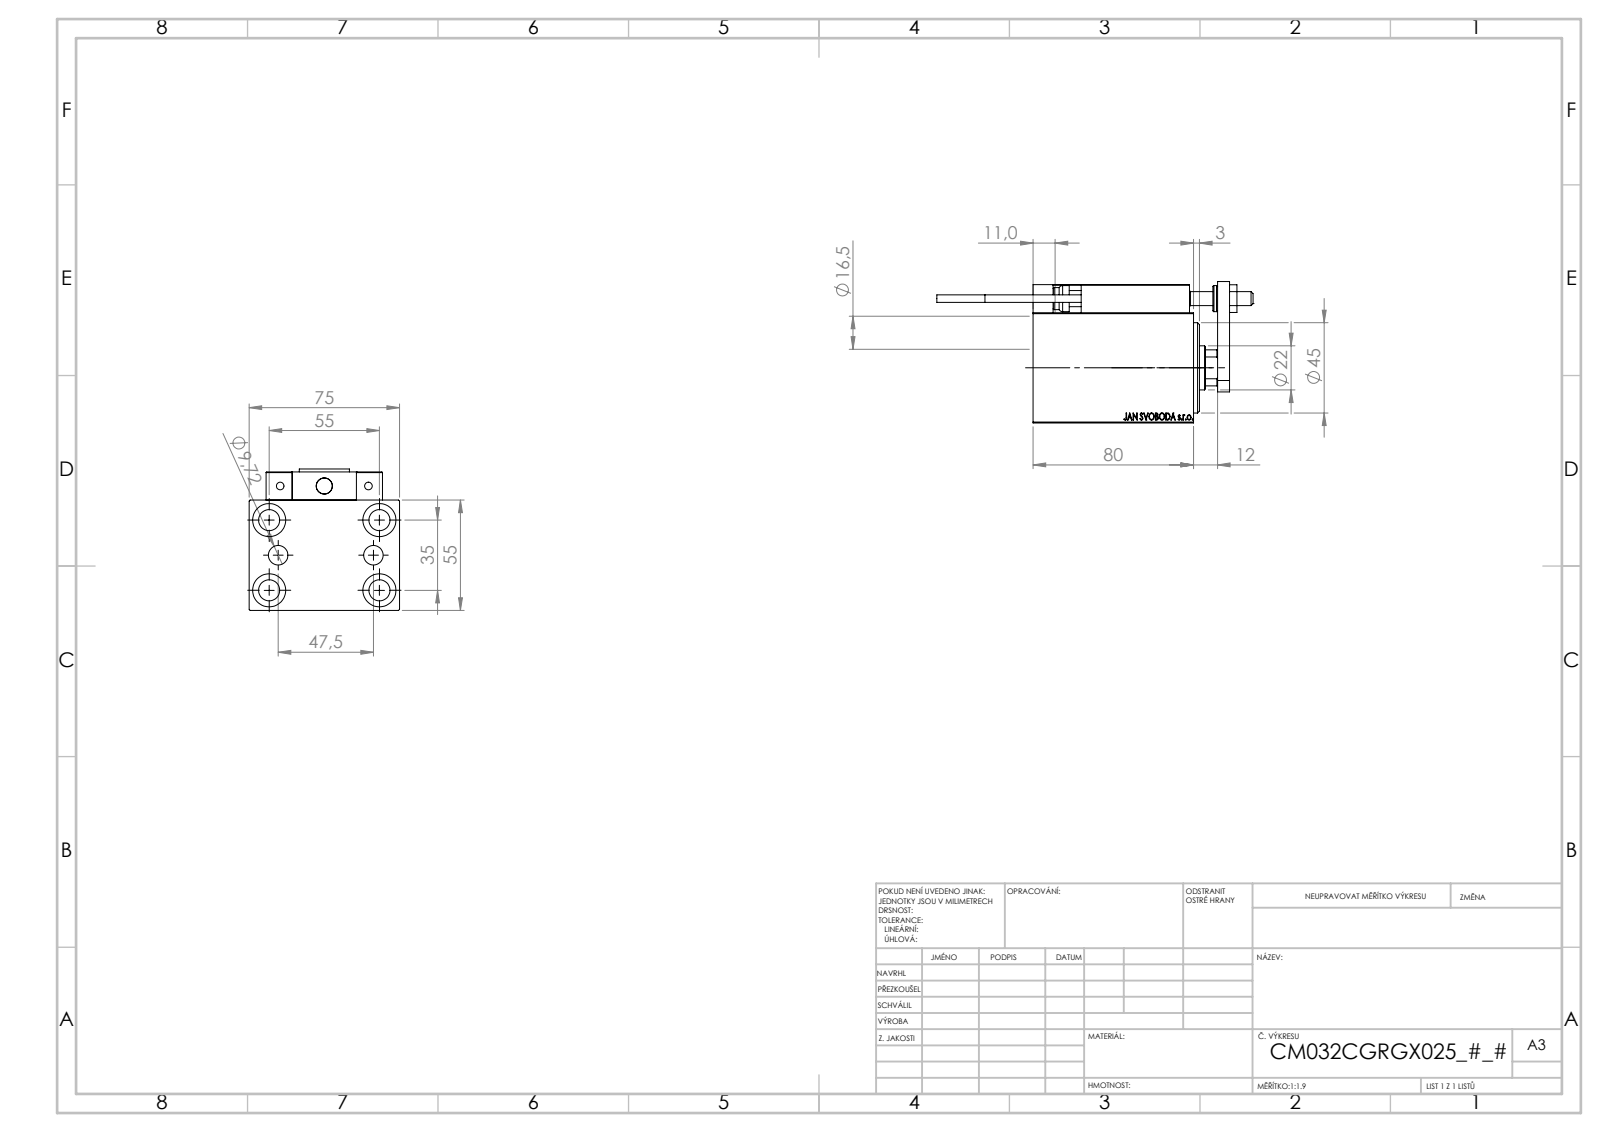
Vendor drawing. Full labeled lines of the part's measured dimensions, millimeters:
Part name (STEP PRODUCT): KONCOVKA; ALLEN BOLT D5; TYC_L79; SWITCH X (+7 more)
STEP written by: SolidWorks 2019 (CONFIG_CONTROL_DESIGN)
Units: millimetres
Bodies: 23 solids, 1278 faces (560 planar, 184 cylindrical, 534 other)
Overall size (bounding box): 157.7 × 75 × 70.5
Volume: 330 899 mm³ · Surface area: 84 600 mm²
Round holes (diameter × count): ⌀4 ×6, ⌀8 ×5, ⌀10.5 ×5, ⌀16.5 ×5, ⌀3.2 ×4, ⌀5 ×2, ⌀9.72 ×2, ⌀7 ×1, ⌀22 ×1, ⌀25.5 ×1, ⌀32 ×1, ⌀34 ×1
Round bosses / shafts (diameter × count): ⌀5 ×2, ⌀3.8 ×2, ⌀13 ×1, ⌀11 ×1
Partial cylindrical surfaces — rounded edges, fillets, slot ends (radius × count): R0.3 ×30, R3 ×2, R10.5 ×1
Main face-to-face distances: 55, 75, 14, 69, 5, 25, 23, 10, 12, 13
Hole centre spacings: 17.9, 32.6, 54.16, 11.37, 20, 23.75, 29.59, 29.69
